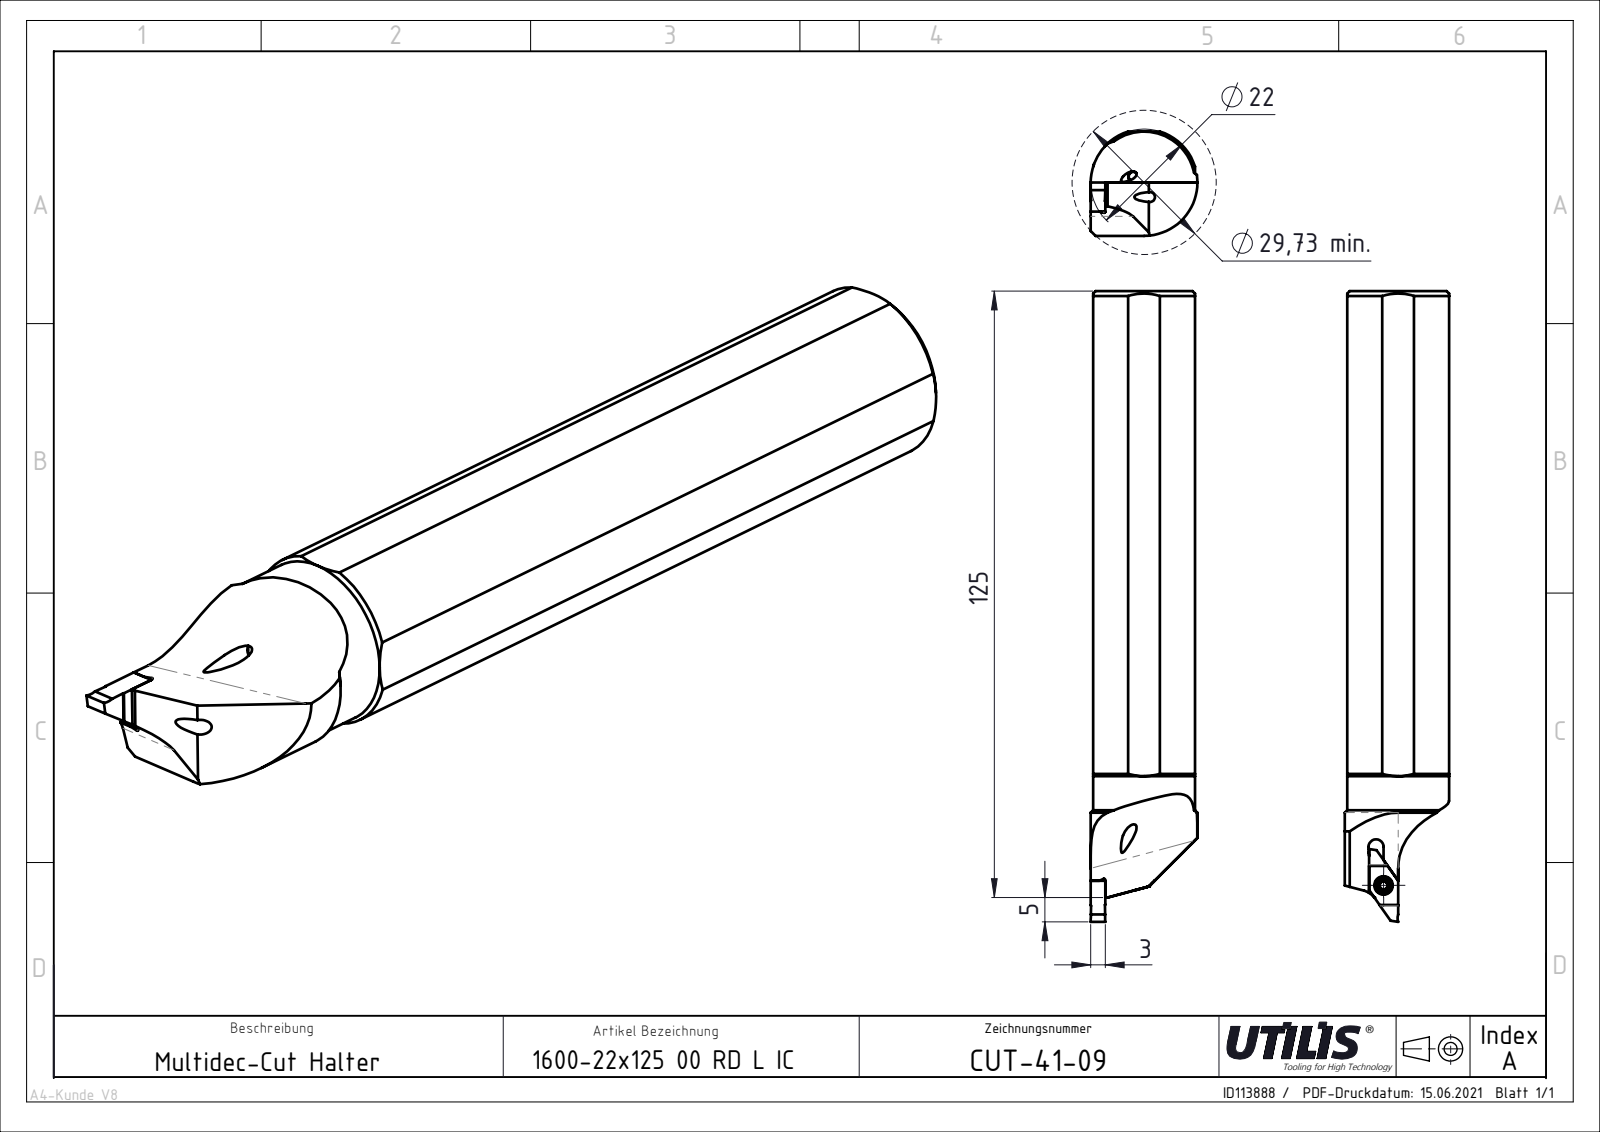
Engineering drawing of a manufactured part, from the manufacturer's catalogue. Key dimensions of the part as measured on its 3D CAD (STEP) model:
Part name (STEP PRODUCT): MSP-7_M2,5X6-TX8 CERATIZIT Schraube; CUT-41-Vorlage 1600-Kunde_Dfaut; CUT-41-Kunde_09; CUT-41-09
STEP written by: SolidWorks 2013 (CONFIG_CONTROL_DESIGN)
Units: millimetres
Bodies: 3 solids, 112 faces (31 planar, 44 cylindrical, 37 other)
Overall size (bounding box): 130 × 22 × 21.5
Volume: 39 400 mm³ · Surface area: 11 329 mm²
Round holes (diameter × count): ⌀2 ×1, ⌀2.05 ×1, ⌀2.2 ×1, ⌀3 ×1, ⌀6 ×1, ⌀8.8 ×1
Round bosses / shafts (diameter × count): ⌀21 ×1, ⌀3.45 ×1, ⌀2.5 ×1
Partial cylindrical surfaces — rounded edges, fillets, slot ends (radius × count): R0.2 ×6, R0.45 ×6, R0.4 ×2, R2.9 ×2, R4 ×1, R11 ×1
Main face-to-face distances: 21, 10.5, 0.5, 21.5, 11, 3, 2.5, 18.5, 0.9, 6
